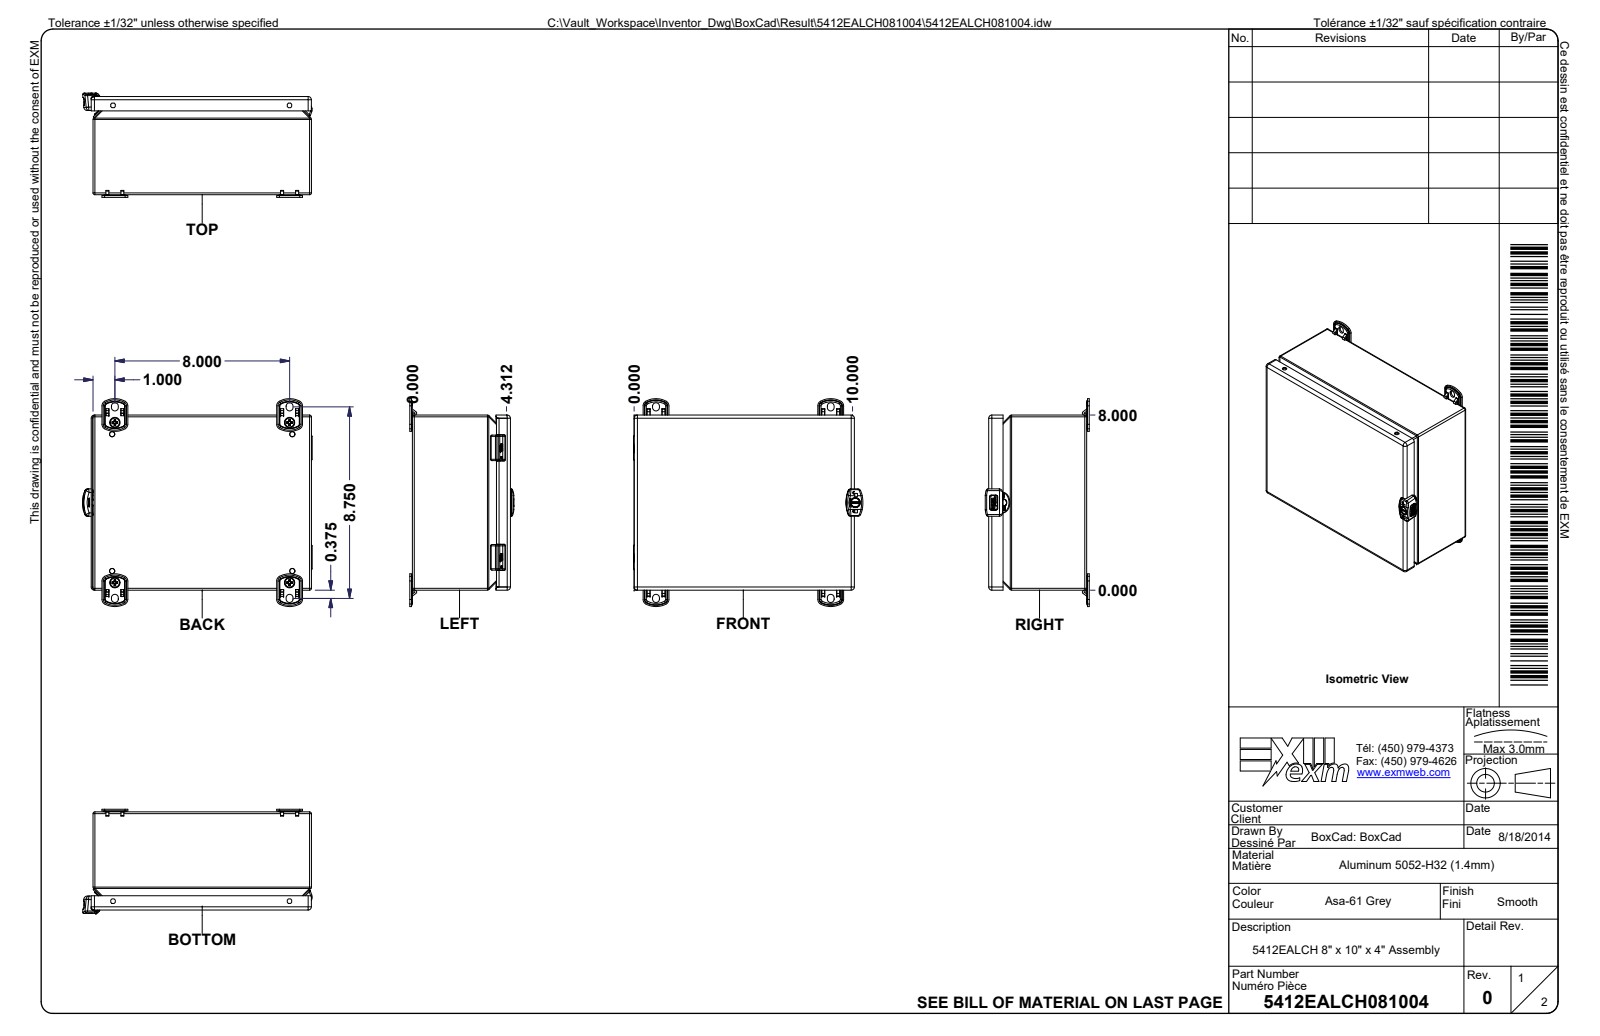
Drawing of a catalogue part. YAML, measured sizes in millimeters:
part_name: "5412EALCH081004; 5412EALCH081004B; 5412EALCH081004B-P; STK-A-70469-1 (+8 more)"
step_written_by: "Autodesk Inventor 2020 (AUTOMOTIVE_DESIGN)"
units: millimeters
bodies: {solids: 51, faces: 6818, planar: 2990, cylindrical: 1592, other: 2236}
overall_size: [266.8, 241.2, 120.9]
volume: 423100
surface_area: 592400
round_holes:
  - {diameter: 5, count: 5}
  - {diameter: 5, count: 4}
  - {diameter: 6, count: 4}
  - {diameter: 8.1, count: 4}
  - {diameter: 4.2, count: 3}
  - {diameter: 4.4, count: 3}
  - {diameter: 6, count: 3}
  - {diameter: 0.8, count: 2}
  - {diameter: 4.4, count: 2}
  - {diameter: 5.1, count: 2}
  - {diameter: 6.1, count: 2}
  - {diameter: 10, count: 2}
round_bosses_or_shafts:
  - {diameter: 5.9, count: 8}
  - {diameter: 12.7, count: 4}
  - {diameter: 6, count: 4}
  - {diameter: 7.6, count: 3}
  - {diameter: 5, count: 3}
  - {diameter: 4.9, count: 3}
  - {diameter: 10, count: 2}
  - {diameter: 0.9, count: 2}
partial_cylinders:
  - {radius: 0.5, count: 213}
  - {radius: 0.3, count: 152}
  - {radius: 1, count: 78}
  - {radius: 0.2, count: 60}
  - {radius: 1.5, count: 55}
  - {radius: 0.1, count: 54}
  - {radius: 0.8, count: 33}
  - {radius: 2.1, count: 24}
face_to_face_distances: [1.3, 1.3, 112.6, 111.3, 201.9, 113.9, 112.6, 6, 7.7, 7.3]
hole_center_spacings: [268.8, 206.8, 262.9, 13.8, 158.8, 172.3, 209.6, 127]
